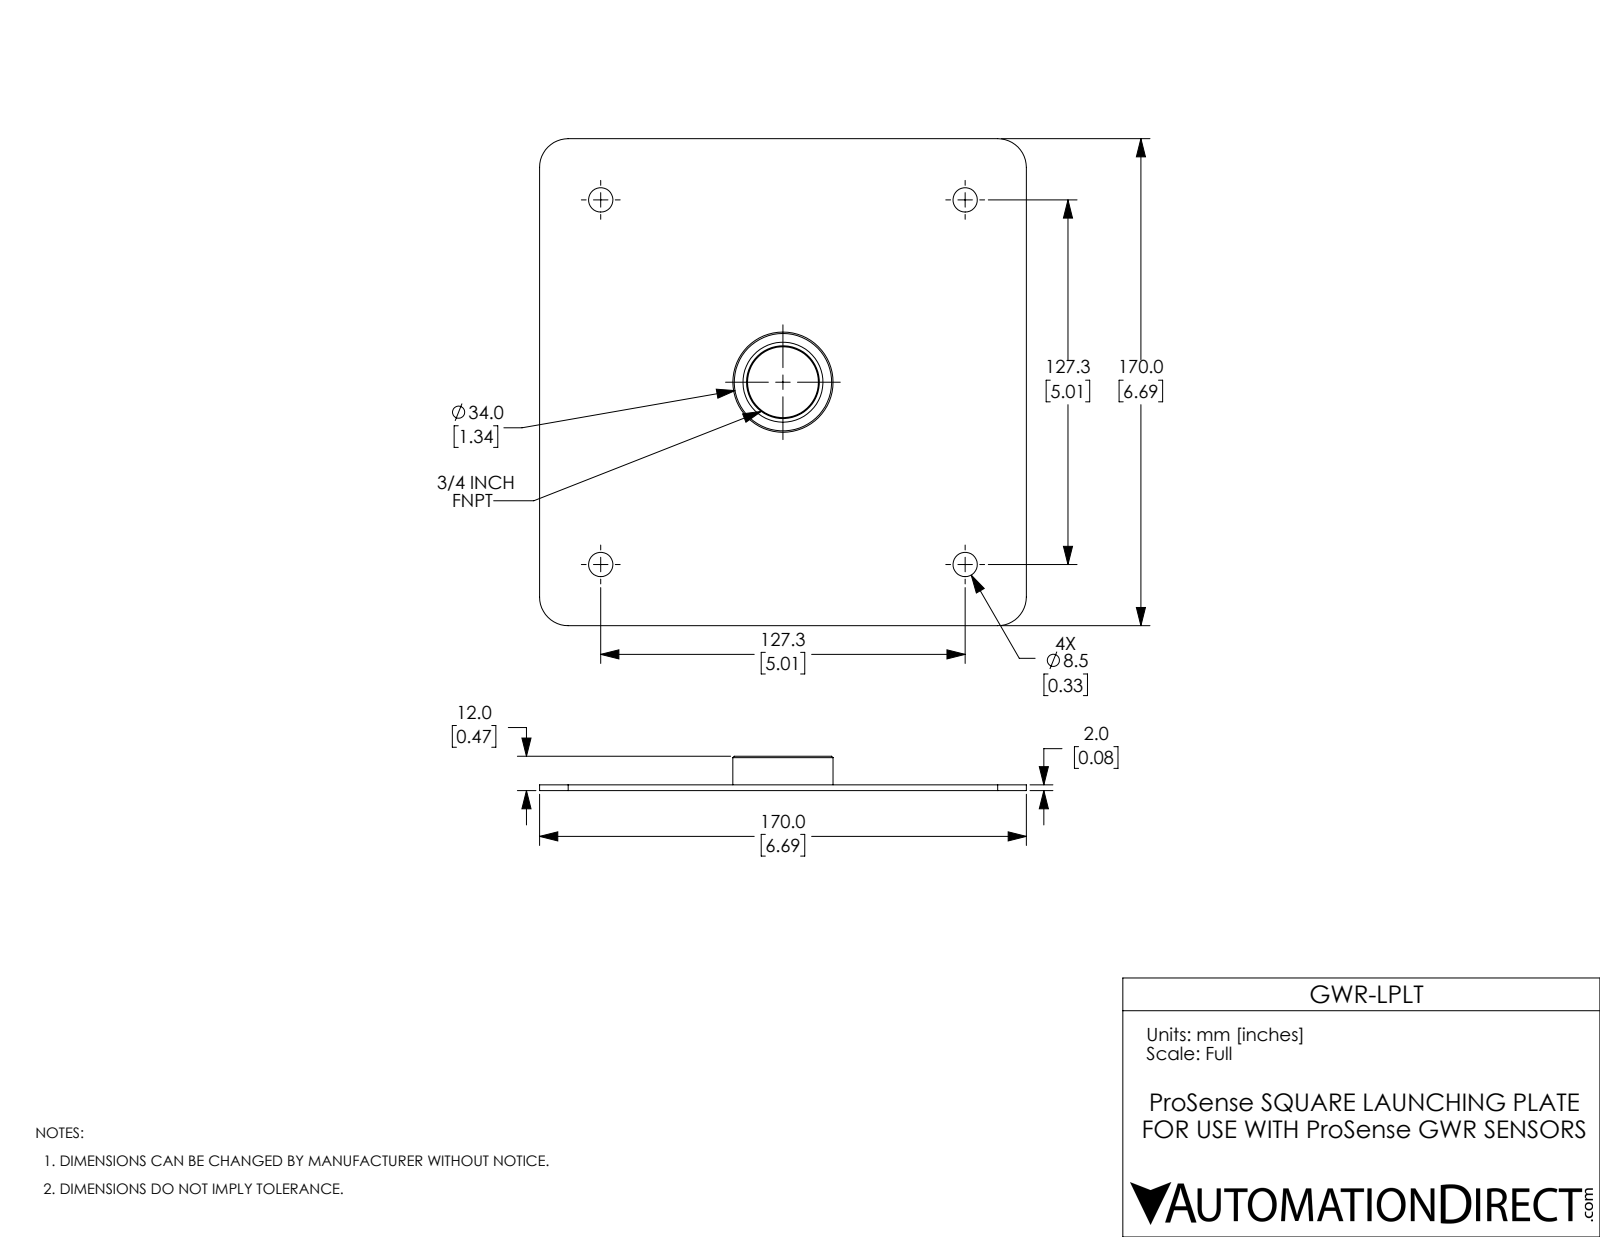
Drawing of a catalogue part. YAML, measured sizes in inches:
part_name: "GWR-LPLT"
step_written_by: "SolidWorks 2017 (AUTOMOTIVE_DESIGN)"
units: inches
bodies: {solids: 1, faces: 32, planar: 8, cylindrical: 16, other: 8}
overall_size: [6.693, 6.693, 0.472]
volume: 3.708
surface_area: 92.63
round_holes:
  - {diameter: 0.335, count: 4}
  - {diameter: 1.378, count: 1}
partial_cylinders:
  - {radius: 0.394, count: 4}
face_to_face_distances: [0.079, 6.693, 0.472, 0.394]
hole_center_spacings: [3.543, 5.011, 7.087]
